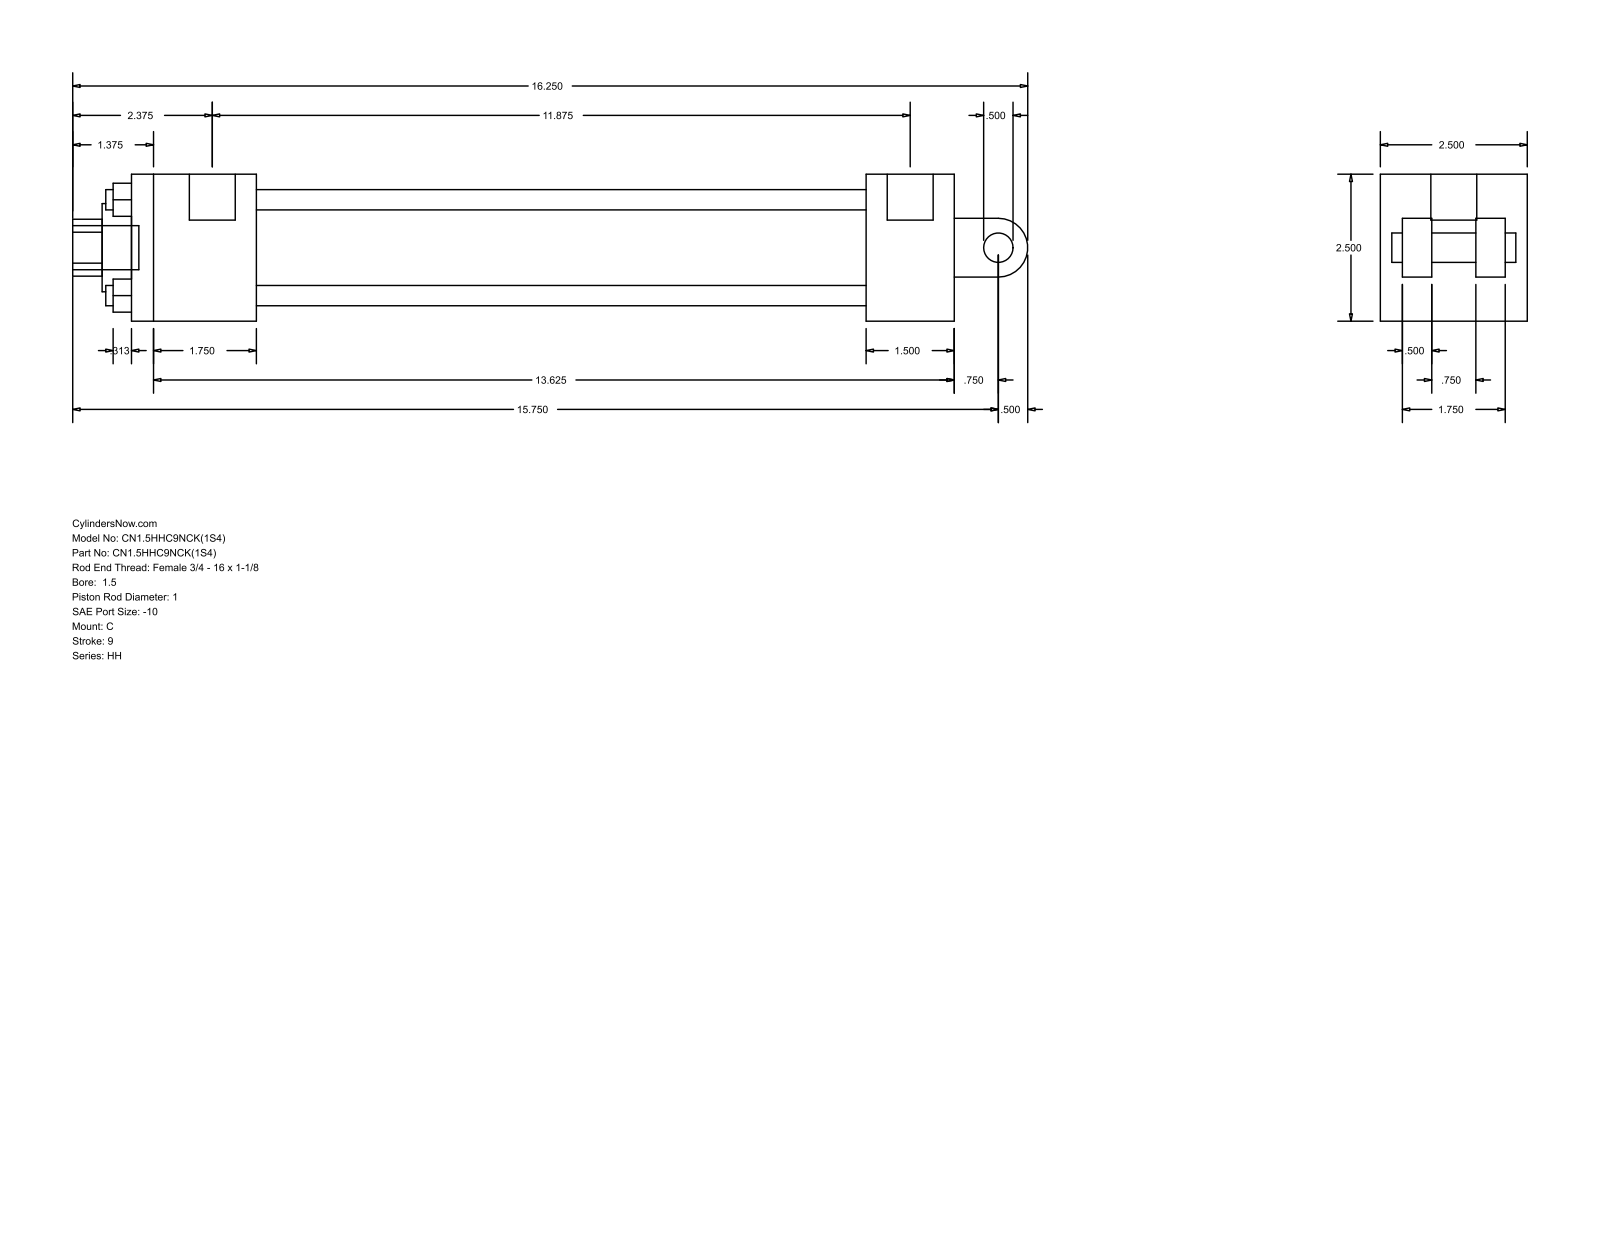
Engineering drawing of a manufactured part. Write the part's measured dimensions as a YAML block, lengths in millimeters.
part_name: "HH_C__0150_1"
step_written_by: "GSSL Pune (CONFIG_CONTROL_DESIGN)"
units: millimeters
bodies: {solids: 0, faces: 99, planar: 70, cylindrical: 29, other: 0}
overall_size: [412.75, 63.5, 63.5]
round_holes:
  - {diameter: 8.76, count: 4}
  - {diameter: 5.56, count: 2}
  - {diameter: 19.84, count: 1}
  - {diameter: 25.4, count: 1}
  - {diameter: 38.1, count: 1}
  - {diameter: 44.45, count: 1}
round_bosses_or_shafts:
  - {diameter: 5.56, count: 2}
  - {diameter: 19.84, count: 1}
  - {diameter: 19.05, count: 1}
  - {diameter: 12.7, count: 1}
partial_cylinders:
  - {radius: 12.29, count: 1}
  - {radius: 12.7, count: 1}
face_to_face_distances: [63.5, 53.98, 263.52, 301.62, 38.1, 317.5, 355.6, 12.7, 22.22, 41.28]
hole_center_spacings: [29.27, 41.4, 58.55, 1.59]
